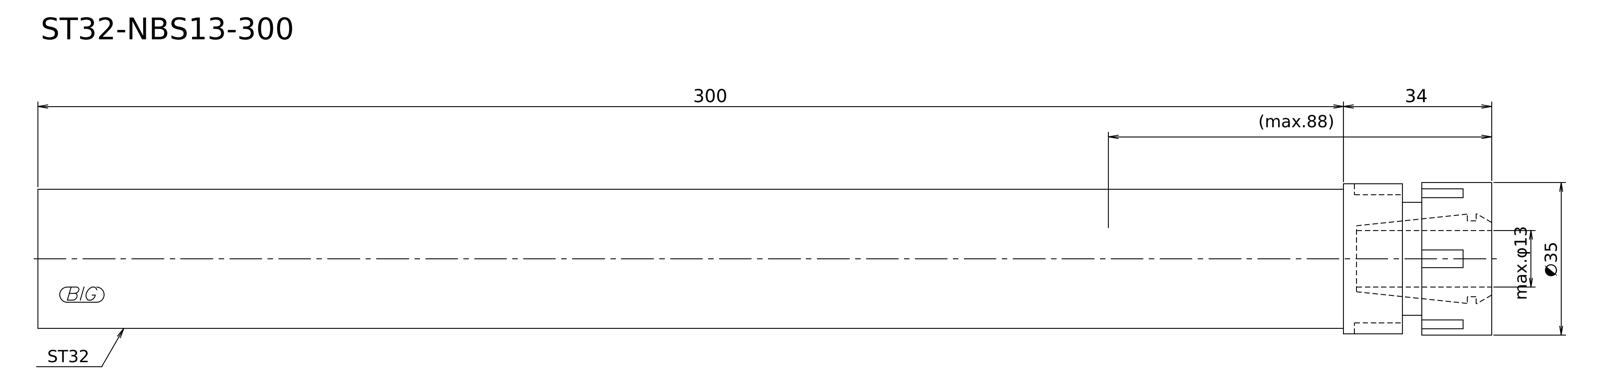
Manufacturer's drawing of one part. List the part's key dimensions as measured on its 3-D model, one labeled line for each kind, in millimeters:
STEP written by: Kubotek KeyCreator V8.5.1 (14335) (CONFIG_CONTROL_DESIGN)
Units: millimetres
Bodies: 1 solid, 9 faces (5 planar, 4 cylindrical, 0 other)
Overall size (bounding box): 334 × 35 × 35
Volume: 271 677 mm³ · Surface area: 36 481 mm²
Round bosses / shafts (diameter × count): ⌀35 ×1, ⌀34.5 ×1, ⌀32 ×1, ⌀26 ×1
Main face-to-face distances: 334, 16, 318, 20.5, 4.5, 313.5, 34, 18, 13.5, 300
